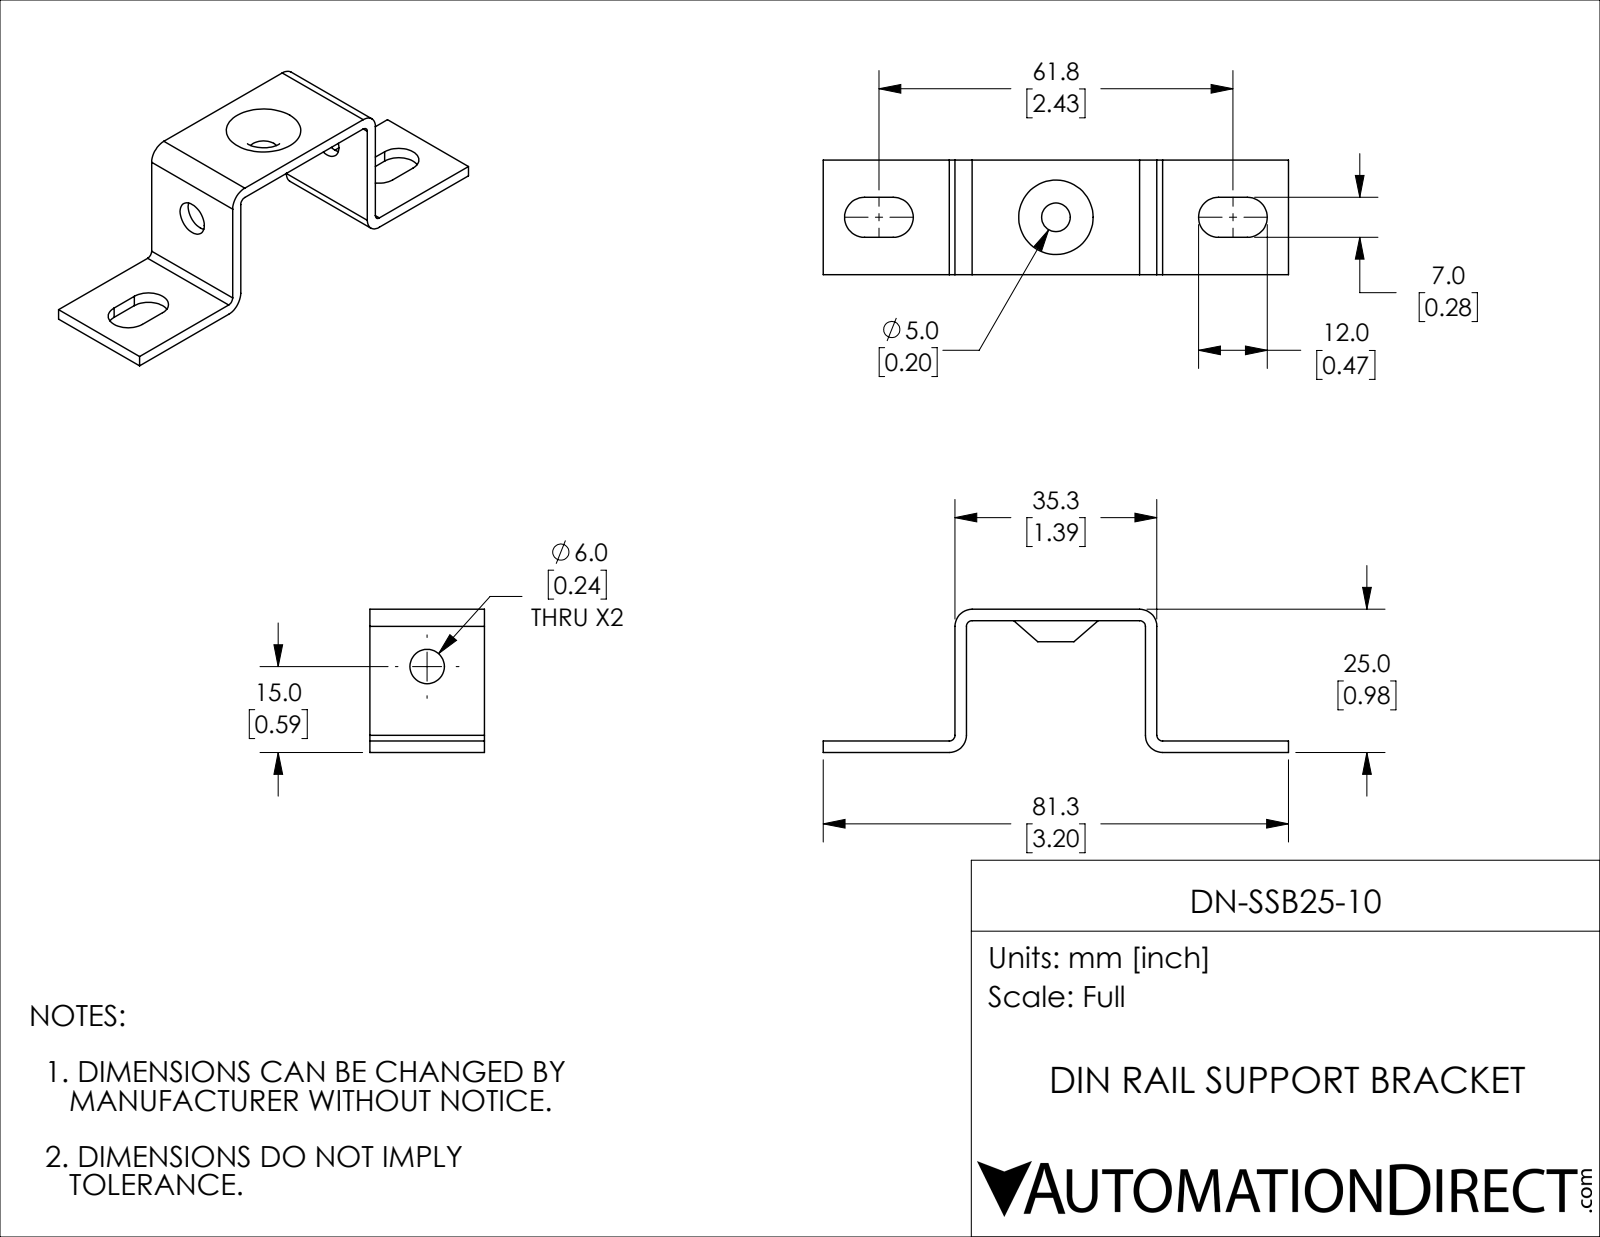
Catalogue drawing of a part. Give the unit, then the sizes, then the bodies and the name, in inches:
Units: inches
Overall size (bounding box): 3.199 × 0.984 × 0.787
Round holes (diameter × count): ⌀0.197 ×1, ⌀0.236 ×1
Partial cylindrical surfaces — rounded edges, fillets, slot ends (radius × count): R0.039 ×4, R0.118 ×4, R0.138 ×4
Main face-to-face distances: 0.079, 0.906, 1.309, 0.984, 0.827, 1.387, 1.23, 0.787, 0.256, 0.531
Volume: 0.287 in³ · Surface area: 8.368 in²
Bodies: 1 solid, 43 faces (19 planar, 20 cylindrical, 4 other)
Part name (STEP PRODUCT): DN-SSB25-10
STEP written by: SolidWorks 2018 (AUTOMOTIVE_DESIGN)
